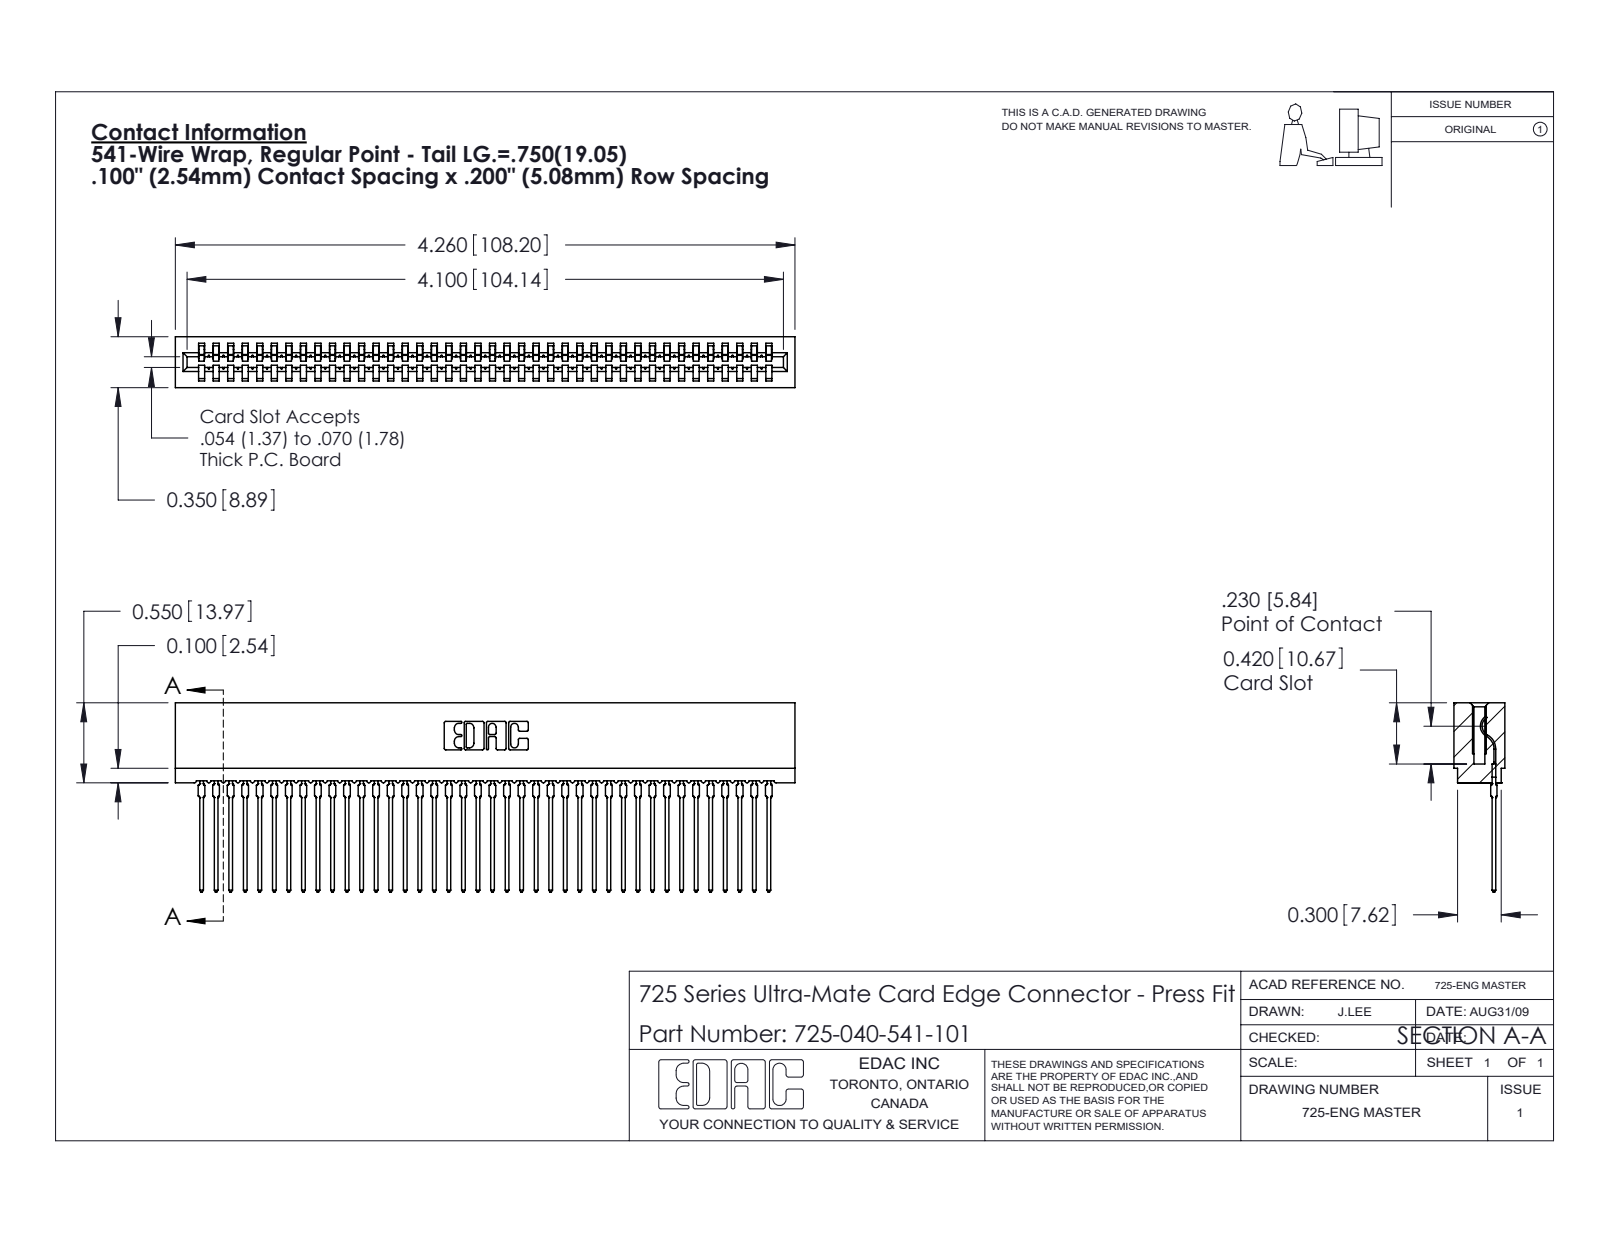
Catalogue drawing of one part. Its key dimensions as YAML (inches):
part_name: "725 Part_Insulator Option - 01; 725-040-541-101; 745-292-001_541"
step_written_by: "SolidWorks 2020 (CONFIG_CONTROL_DESIGN)"
units: inches
bodies: {solids: 41, faces: 4575, planar: 2735, cylindrical: 800, other: 1040}
overall_size: [4.26, 1.301, 0.35]
volume: 0.512
surface_area: 26.19
partial_cylinders:
  - {radius: 0.015, count: 80}
  - {radius: 0.021, count: 80}
  - {radius: 0.01, count: 22}
  - {radius: 0.007, count: 6}
  - {radius: 0.031, count: 6}
  - {radius: 0.005, count: 4}
  - {radius: 0.011, count: 4}
  - {radius: 0.026, count: 3}
face_to_face_distances: [0.35, 0.2, 0.063, 0.287, 0.1, 0.212, 0.138, 0.045, 0.305, 0.093]
